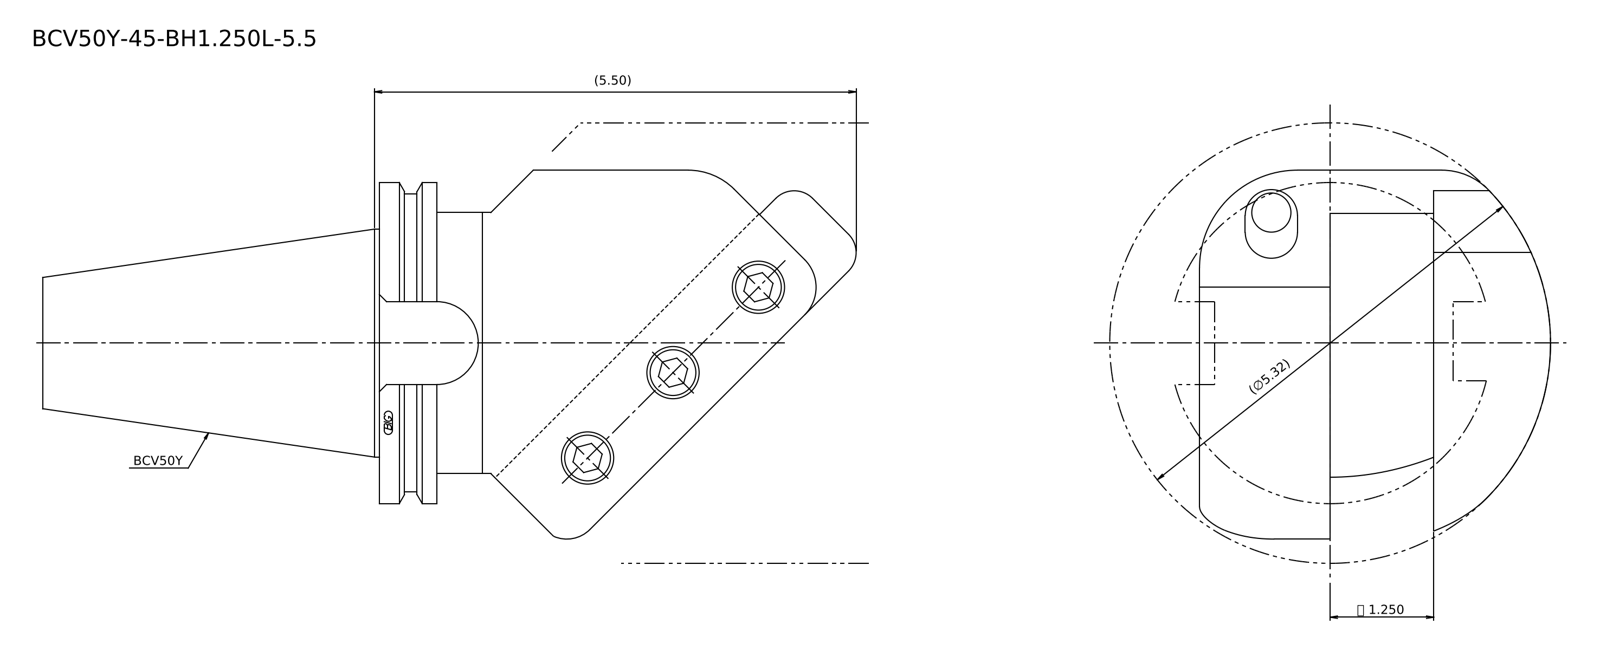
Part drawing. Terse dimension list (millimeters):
written by: Kubotek KeyCreator 2011 V10.0.2 (22737) (automotive_design)
unit: mm
bodies: 1 solid, 29 faces (15 planar, 10 cylindrical, 4 other)
size: 252.43 × 116.73 × 116.71
volume: 1 097 000 mm³; area: 83 691 mm²
bosses: 1× ⌀98.42, 1× ⌀91.29, 1× ⌀80, 1× ⌀69.85
rounds: 1× R20, 1× R30, 1× R67.5
face distances: 71.75, 40, 31.75, 31.74, 17.55, 120.65, 103.1, 15, 31.49, 6.01
